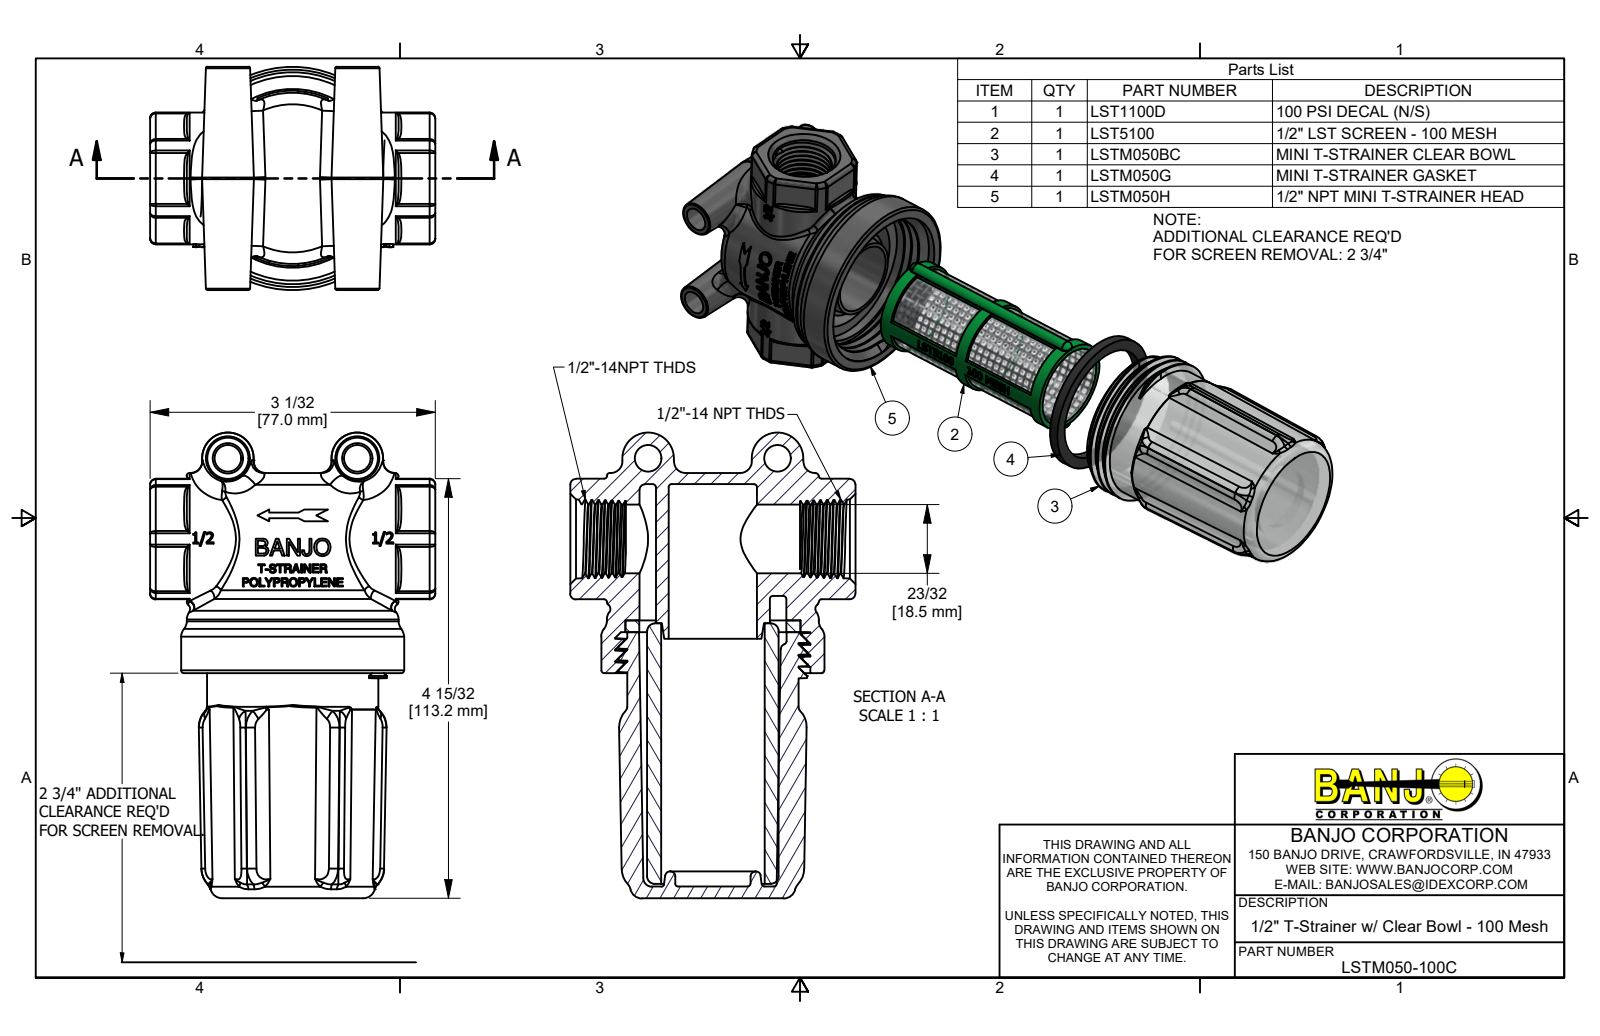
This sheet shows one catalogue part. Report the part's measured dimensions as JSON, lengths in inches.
{"part_name": "LSTM050-100C; LSTM050H; LSTM050G; LST5100 (+1 more)", "step_written_by": "Autodesk Inventor 2019 (AUTOMOTIVE_DESIGN)", "units": "inches", "bodies": {"solids": 4, "faces": 1383, "planar": 563, "cylindrical": 193, "other": 627}, "overall_size": [24.12, 4.947, 2.37], "volume_in3": 8.154, "surface_area_in2": 190.7, "round_holes": [[0.73, 1], [0.8, 1], [0.937, 1], [1.101, 1], [1.56, 1], [1.563, 1], [1.891, 1], [2.073, 1]], "round_bosses_or_shafts": [[2.37, 1], [2.25, 1], [2.001, 1], [1.861, 1], [1.86, 1], [1.82, 1], [1.4, 1], [1.23, 1]], "partial_cylinders_radius": [[0.06, 24], [0.03, 4], [0.08, 4], [0.05, 3], [0.084, 2], [0.26, 1], [0.546, 1], [0.576, 1]], "face_to_face_distances": [2.825, 2.95, 0.125, 1.28, 4.515, 1.69, 1.565, 4.397, 1.572, 1.447]}
